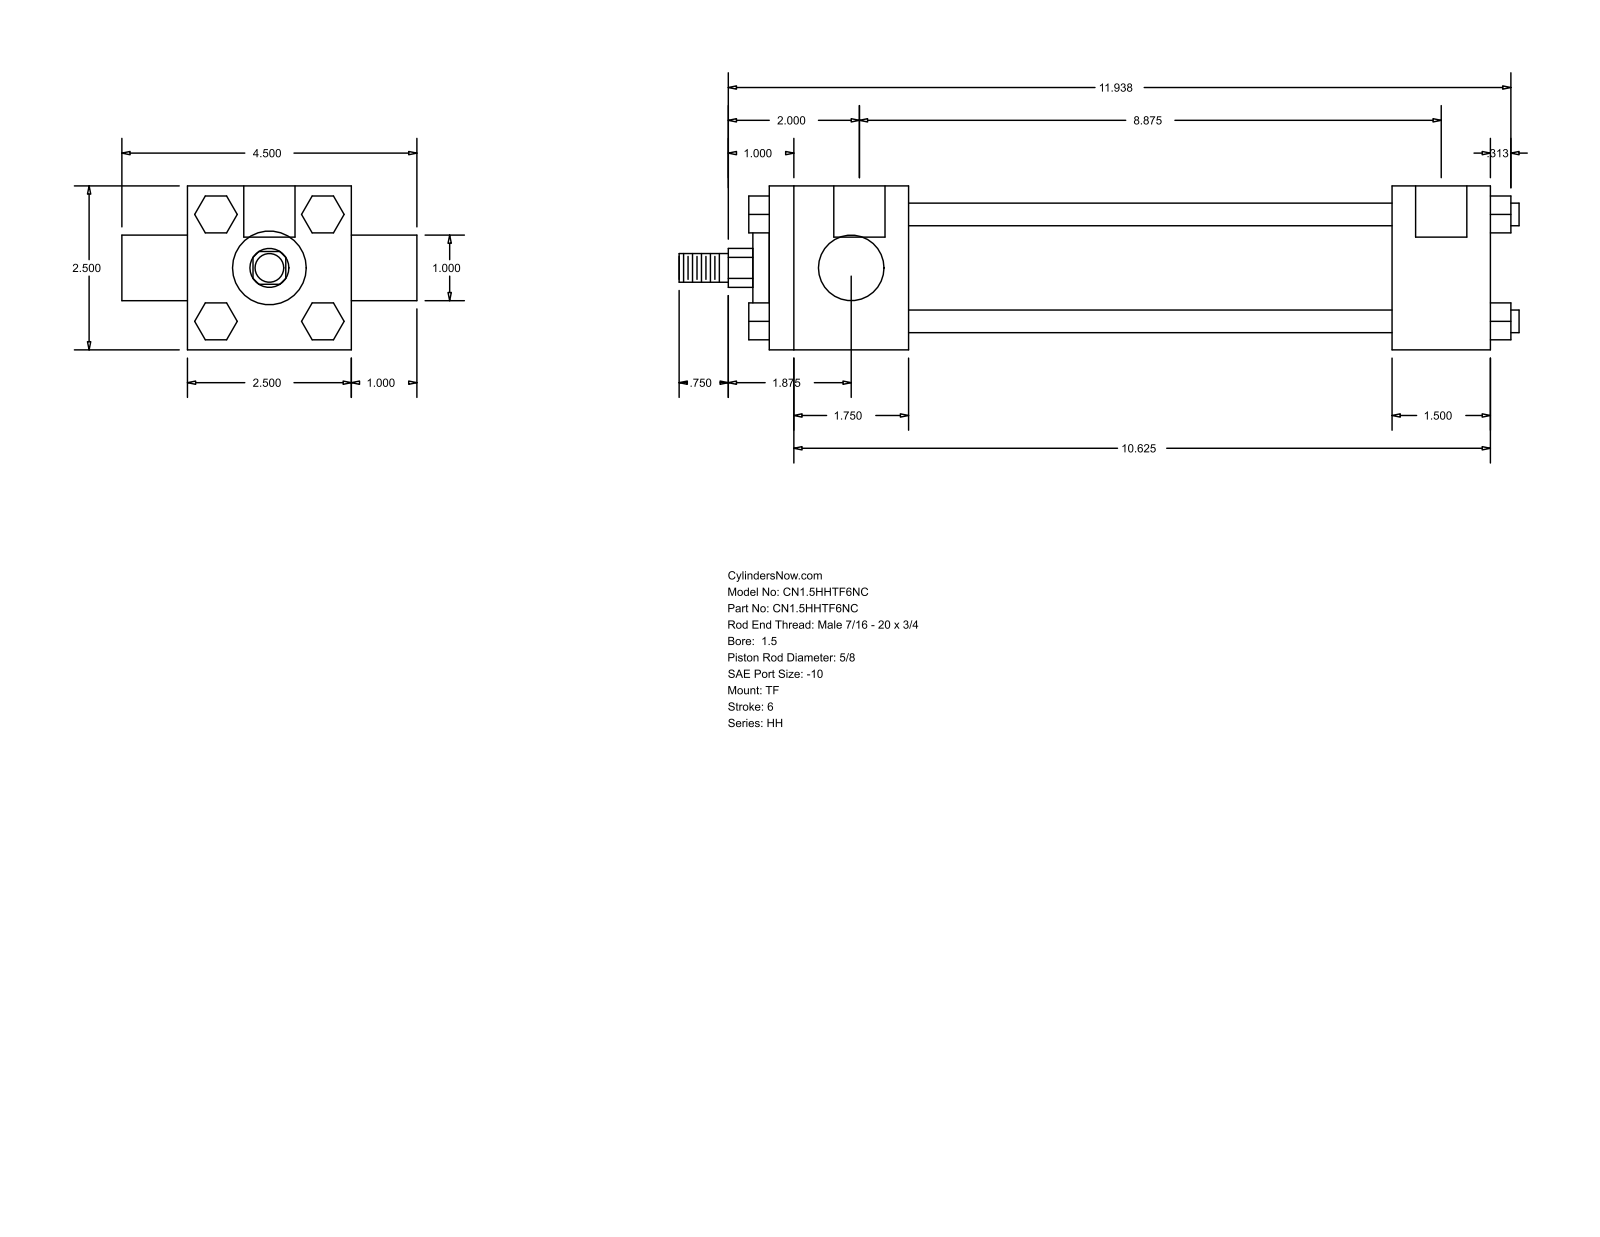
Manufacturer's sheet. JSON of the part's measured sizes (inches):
{"part_name": "HH_TF__0150_0.625", "step_written_by": "GSSL Pune (CONFIG_CONTROL_DESIGN)", "units": "inches", "bodies": {"solids": 0, "faces": 120, "planar": 92, "cylindrical": 28, "other": 0}, "overall_size": [12.813, 4.5, 2.5], "round_holes": [[0.219, 3], [0.781, 2]], "round_bosses_or_shafts": [[0.345, 4], [1.75, 1], [1.125, 1], [1, 1], [0.625, 1], [0.437, 1]], "partial_cylinders_radius": [[0.297, 1]], "face_to_face_distances": [2.5, 11, 2.125, 8.875, 9.5, 7.375, 1.5, 1, 3.5, 0.815], "hole_center_spacings": [0.062, 0.063, 8.875, 8.937, 8.938, 9]}
